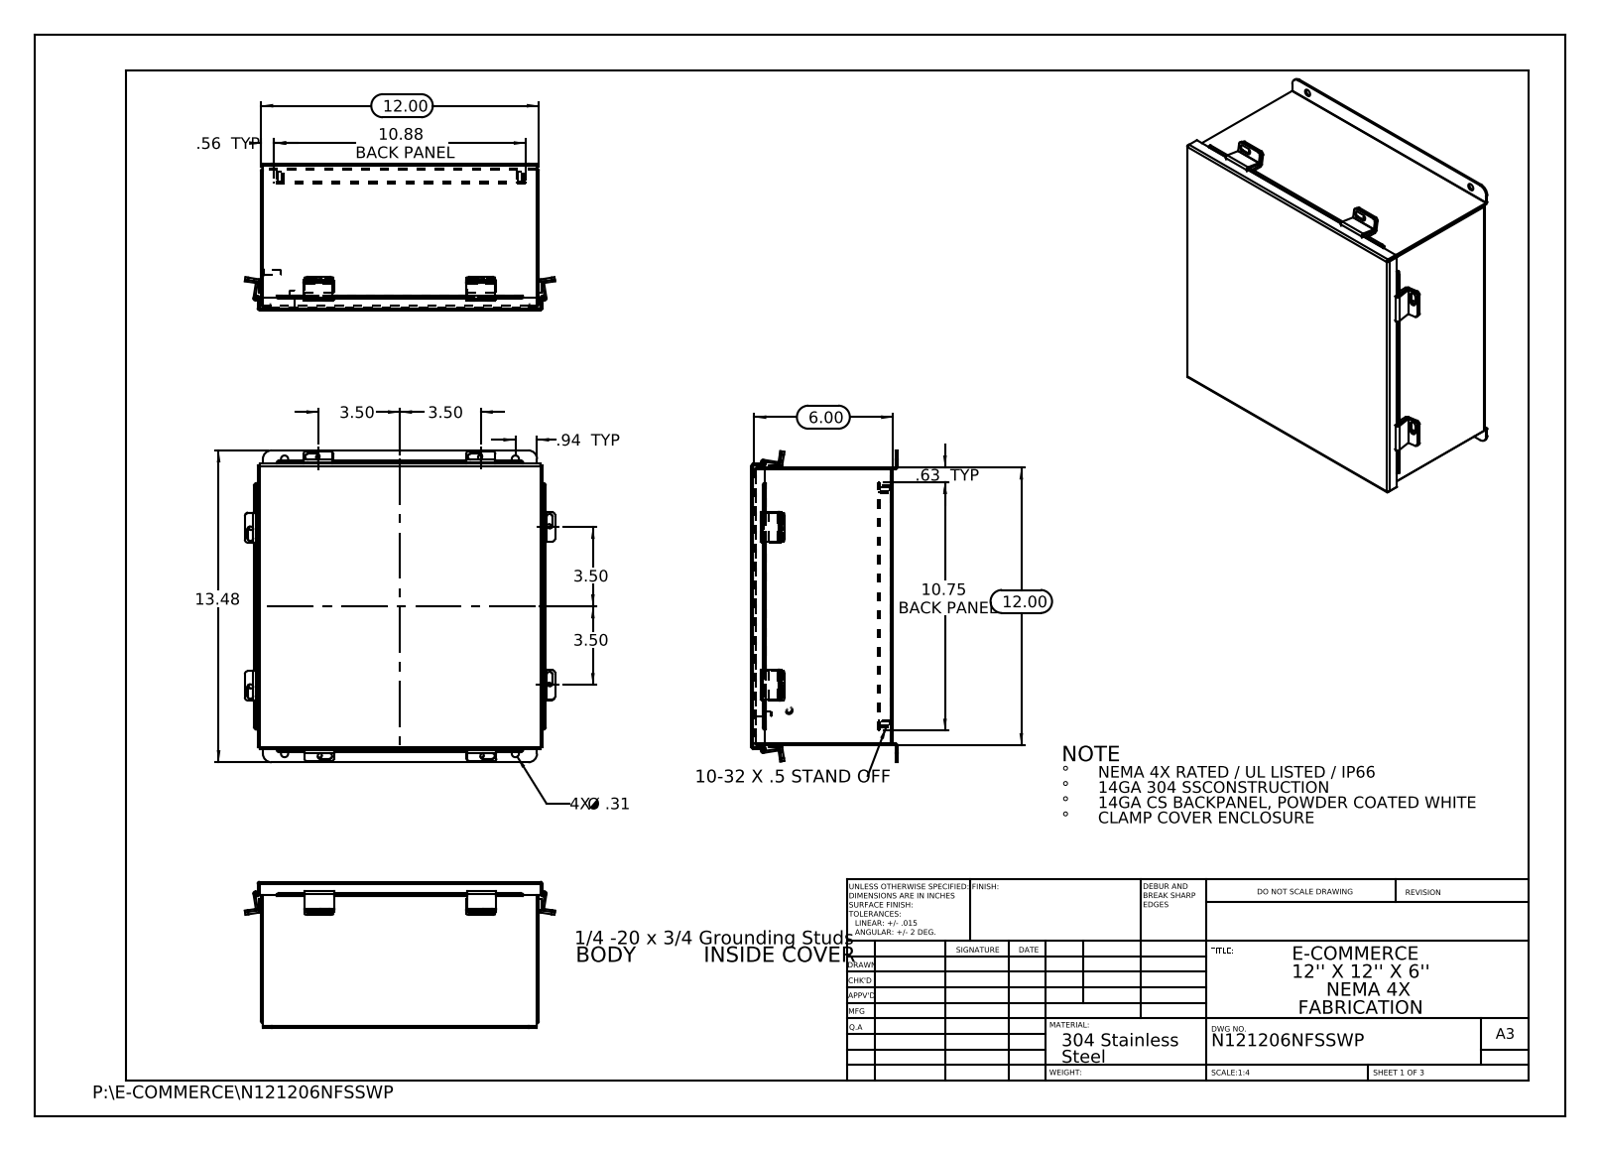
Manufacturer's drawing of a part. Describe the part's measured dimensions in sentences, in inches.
The part is named "N121206NFSSWP Hinge Cover Side JIC; N121206NFSSWP Hinge Body Side; N121206NFSSWP _JIC Hinge; N121206NFSSWP JIC Backpanel (+8 more)". Its 3-D file was written by "SolidWorks 2013 (CONFIG_CONTROL_DESIGN)". It is 27 solids with 774 faces: 499 planar, 255 cylindrical and 20 other. Overall it measures 13.476 by 13.072 by 6.39 inches. Its volume is 59.94 cubic inches and its surface area 1 634 square inches. Round holes: 10 of diameter 0.25, 4 of diameter 0.187, 4 of diameter 0.312, 1 of diameter 0.125, 1 of diameter 0.125, 1 of diameter 0.373, 1 of diameter 0.375. Round bosses or shafts: 4 of diameter 0.313, 2 of diameter 0.315, 2 of diameter 0.236, 1 of diameter 0.273, 1 of diameter 0.25. Partial cylindrical surfaces (rounded edges, fillets, slot ends): 21 of radius 0.125, 13 of radius 0.013, 12 of radius 0.009, 12 of radius 0.088, 12 of radius 0.133, 6 of radius 0.083, 6 of radius 0.1, 4 of radius 0.375. The main face-to-face distances are 0.075, 11.925, 6.128, 12, 11.85, 6.053, 6.203, 0.074, 0.575, 0.5. The hole center spacings are 1.315, 10.258, 11.428, 15.3, 7, 9.976, 10.126, 10.375.
